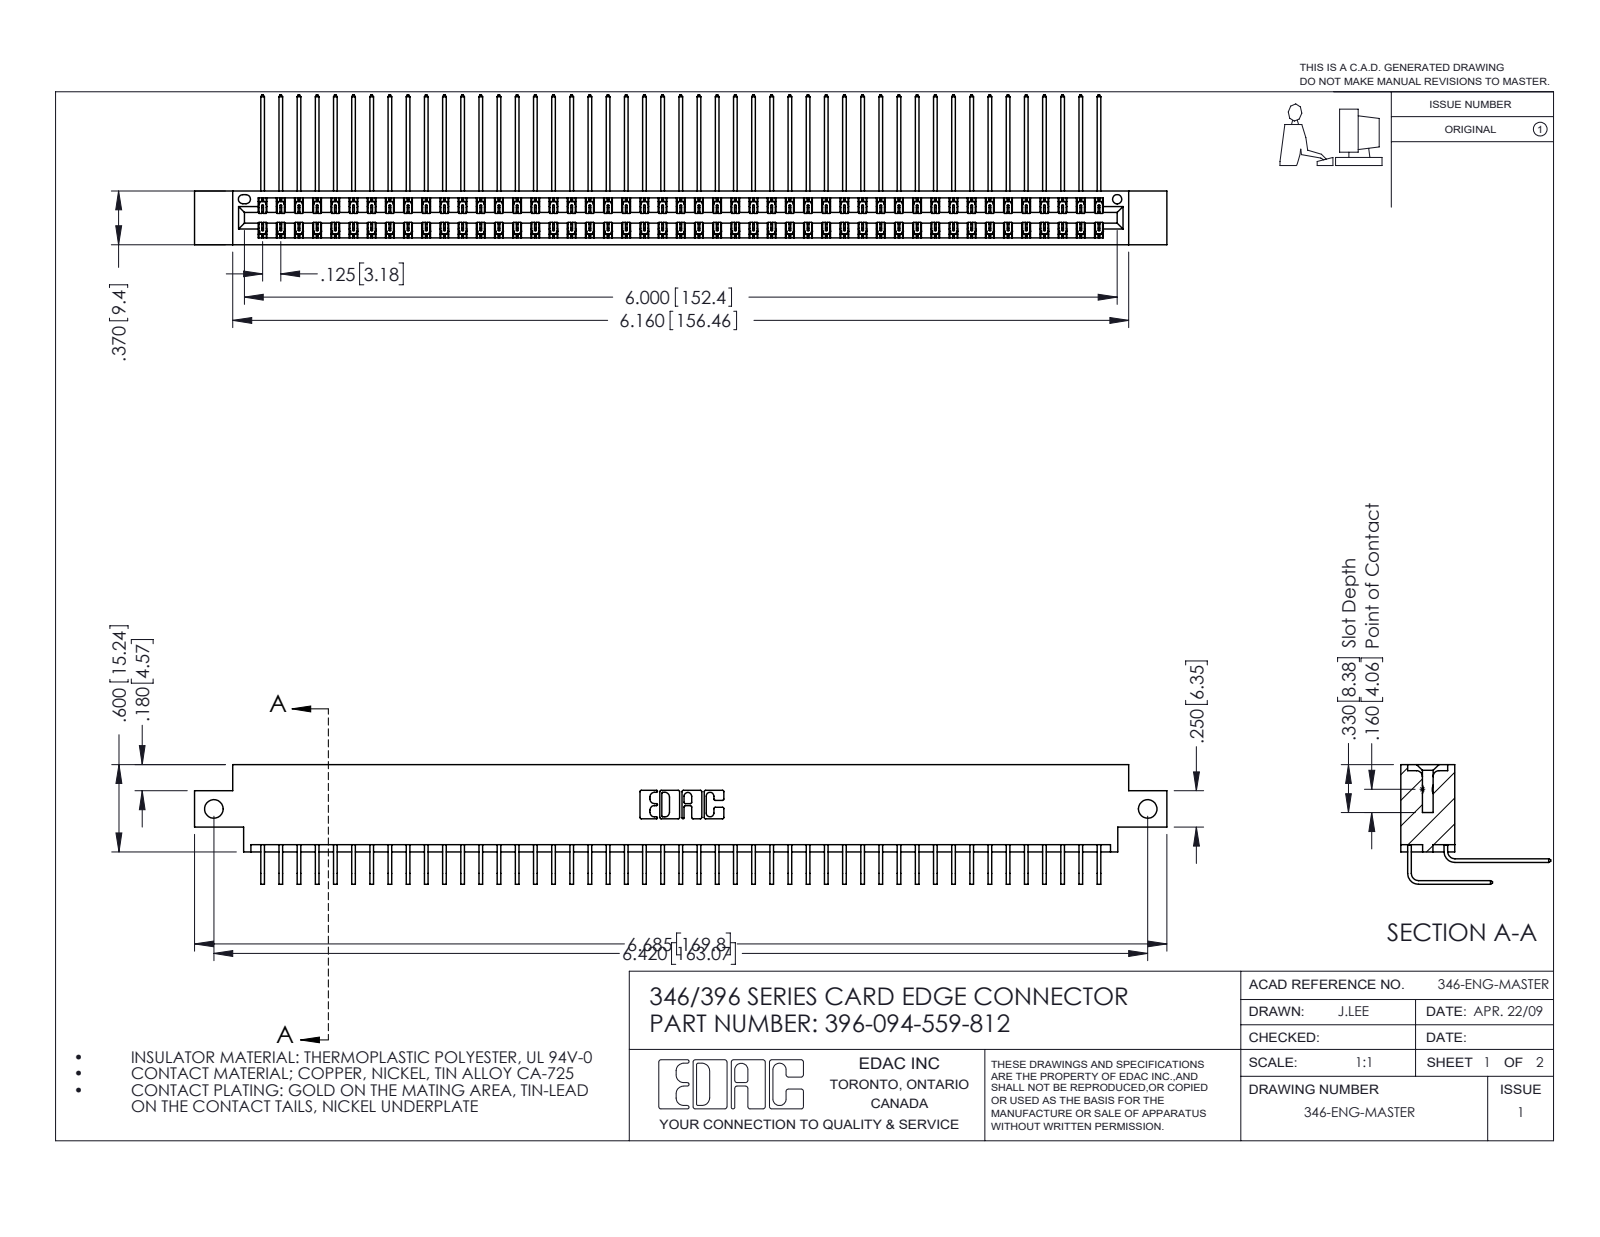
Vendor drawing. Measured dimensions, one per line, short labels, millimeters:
name: 396-094-559-812; 345-292-001_559 Tail - 2; 345-292-001_558 559 Tail - 1; 346 Part_0.170 Offset - Side Mount
written by: SolidWorks 2016 (CONFIG_CONTROL_DESIGN)
unit: mm
bodies: 95 solids, 5202 faces (3558 planar, 1644 cylindrical, 0 other)
size: 169.8 × 26.2 × 20.9
volume: 16 900 mm³; area: 25 950 mm²
holes: 2× ⌀3.3, 1× ⌀1.6
rounds: 141× R0.2, 22× R0.3, 6× R0.2, 6× R0.8, 3× R0.7, 2× R0.4, 2× R0.6, 2× R0.6
face distances: 1.2, 8.2, 0.6, 9.4, 6.4, 1.8, 7.6, 7, 3.8, 5.6
hole spacings: 163.1
